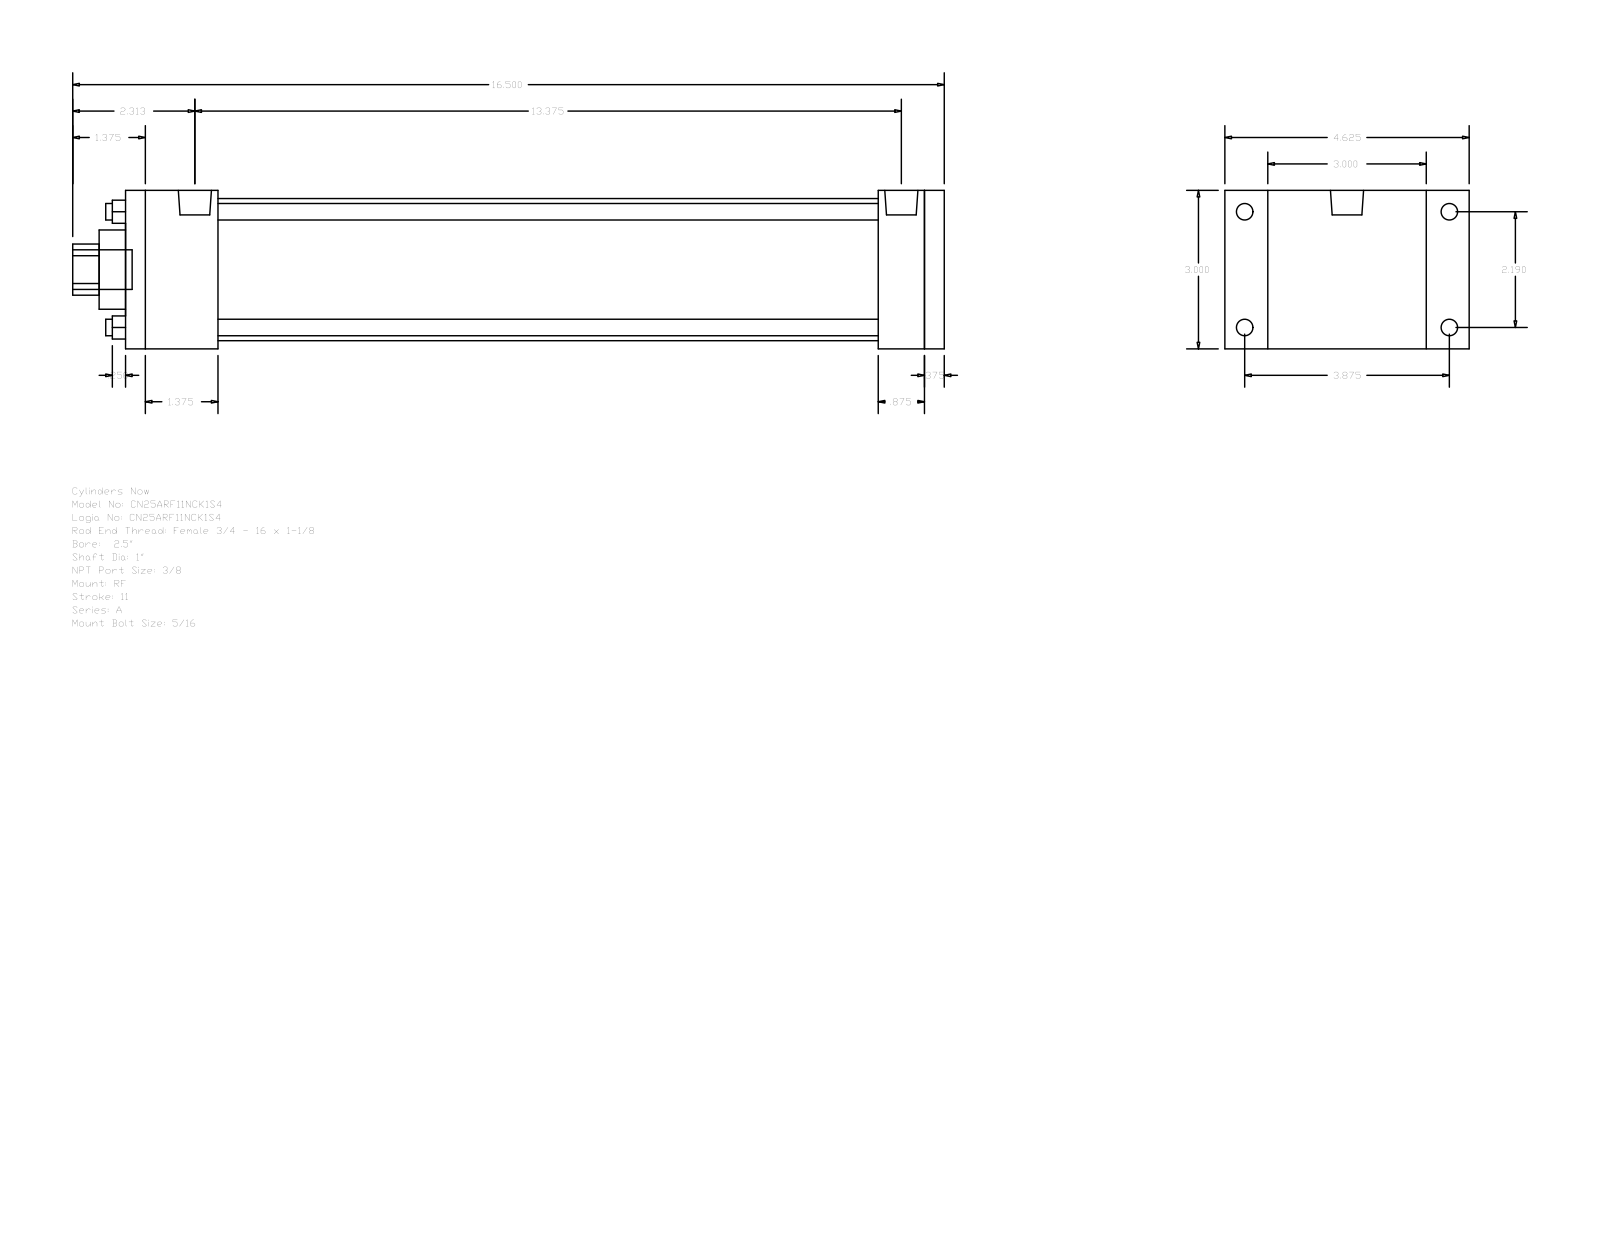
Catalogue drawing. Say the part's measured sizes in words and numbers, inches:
The part is named "A_RF__0250_1". Its 3-D file was written by "GSSL Pune (CONFIG_CONTROL_DESIGN)". It is 0 solids with 92 faces: 64 planar, 28 cylindrical and 0 other. Overall it measures 16.5 by 4.625 by 3 inches. Round holes: 4 of diameter 0.313, 1 of diameter 1, 1 of diameter 1.5, 1 of diameter 2.69. Round bosses or shafts: 4 of diameter 0.313, 4 of diameter 0.219, 2 of diameter 0.627, 1 of diameter 0.75. Partial cylindrical surfaces (rounded edges, fillets, slot ends): 1 of radius 0.484. The main face-to-face distances are 3, 15.5, 0.375, 15.125, 1.75, 14.25, 12.5, 13.375, 13.75, 0.875. The hole center spacings are 1.548, 2.19, 3.097.
